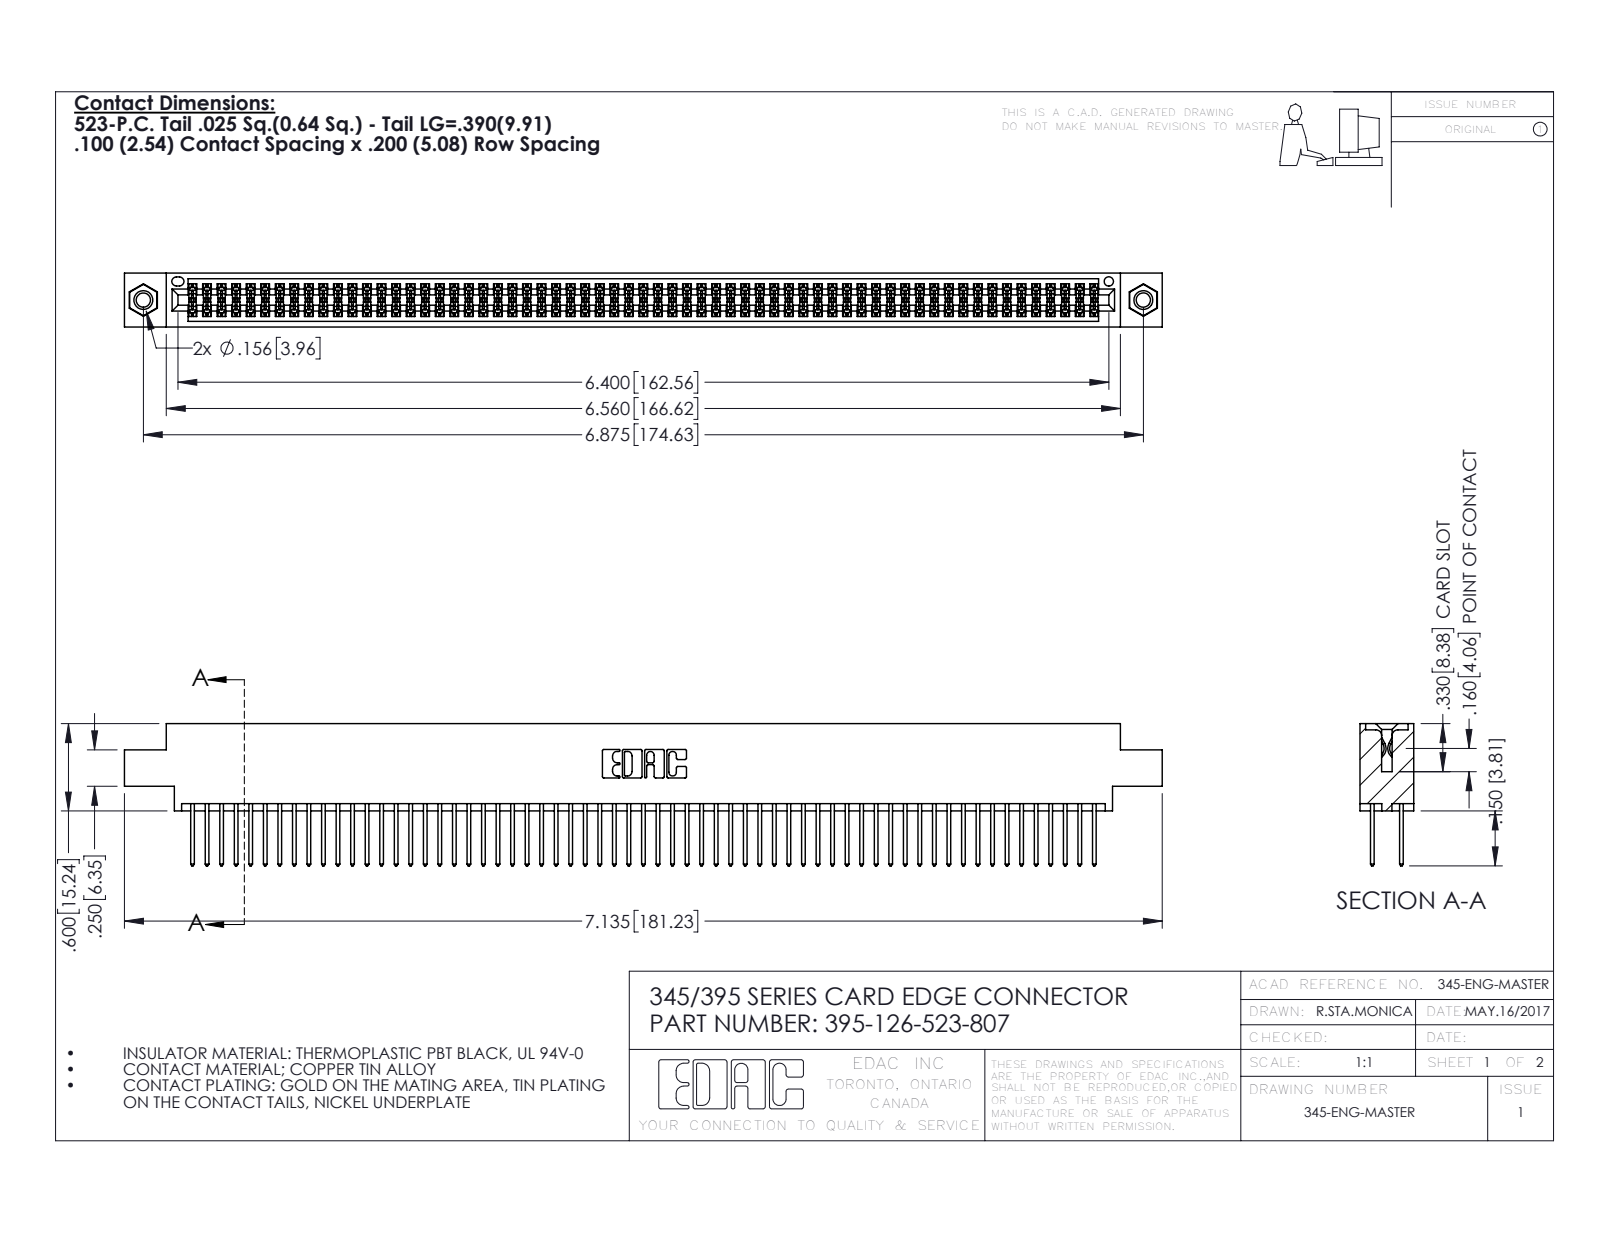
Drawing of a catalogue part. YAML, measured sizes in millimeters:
part_name: "345 Part_0.170 Offset - 0.156 Dia-TI; 345-250-001_345-250-005-103; 395-126-523-807; 345-292-001_345-293-123"
step_written_by: "SolidWorks 2016 (CONFIG_CONTROL_DESIGN)"
units: millimeters
bodies: {solids: 129, faces: 6490, planar: 4274, cylindrical: 2200, other: 16}
overall_size: [181.2, 24.8, 9.4]
volume: 17930
surface_area: 28240
round_holes:
  - {diameter: 2.5, count: 2}
  - {diameter: 3.2, count: 2}
  - {diameter: 4, count: 2}
  - {diameter: 1.6, count: 1}
round_bosses_or_shafts:
  - {diameter: 3.9, count: 2}
partial_cylinders:
  - {radius: 0.2, count: 189}
  - {radius: 0.3, count: 126}
  - {radius: 0.3, count: 22}
  - {radius: 0.2, count: 6}
  - {radius: 0.8, count: 6}
  - {radius: 0.7, count: 3}
  - {radius: 0.4, count: 2}
  - {radius: 0.5, count: 2}
face_to_face_distances: [1.8, 7.6, 5.1, 2.5, 6.9, 0.6, 9.4, 5.7, 4.4, 3.8]
hole_center_spacings: [6.9, 168.6, 174.6]
